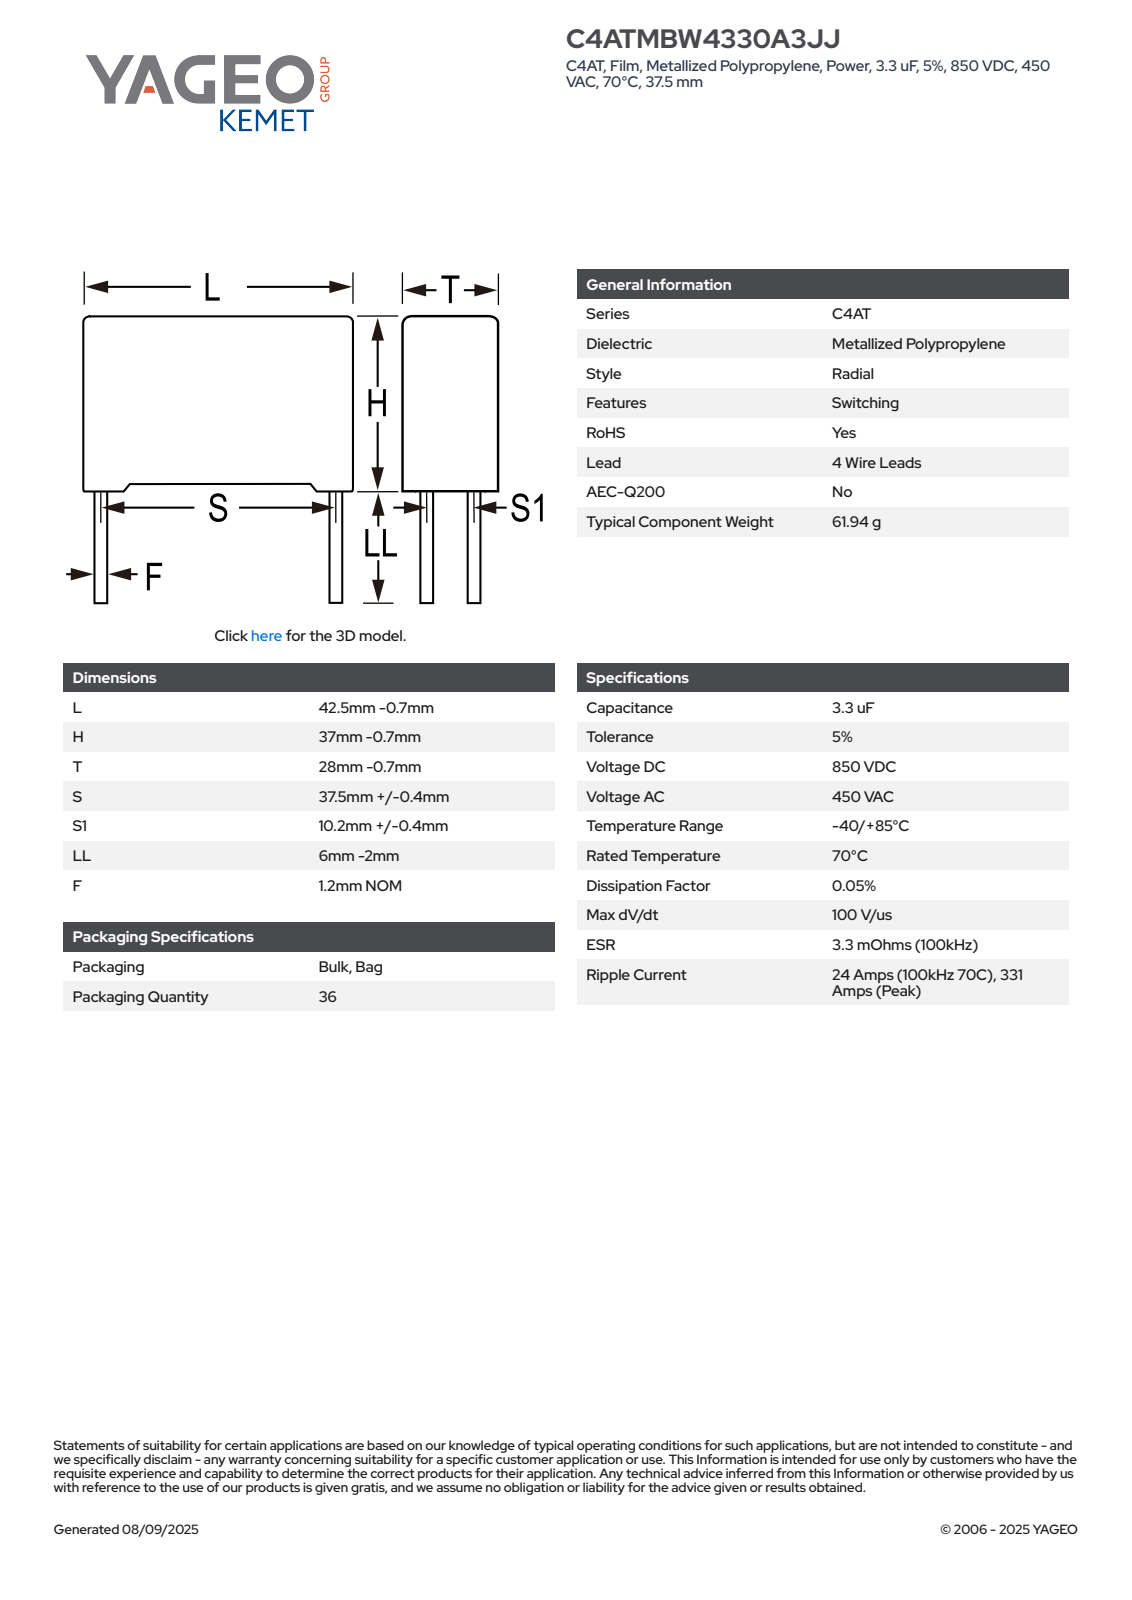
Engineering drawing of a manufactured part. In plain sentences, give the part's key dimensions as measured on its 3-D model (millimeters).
The part is named "CFP_RB4_42.5X37X28_L41.8H36.3T27.3S37.5S110.2LL4F1.2". Its 3-D file was written by "SolidWorks 2014 (AUTOMOTIVE_DESIGN)". It is 4 solids with 91 faces: 83 planar, 8 cylindrical and 0 other. Overall it measures 41.8 by 40.3 by 27.3 millimeters. Its volume is 40 364 cubic millimeters and its surface area 7 500 square millimeters. Round bosses or shafts: 4 of diameter 1.2. The main face-to-face distances are 27.3, 35.23, 41.8, 1.07, 36.3, 1.68, 27.31, 40.12, 38.44, 25.62.
